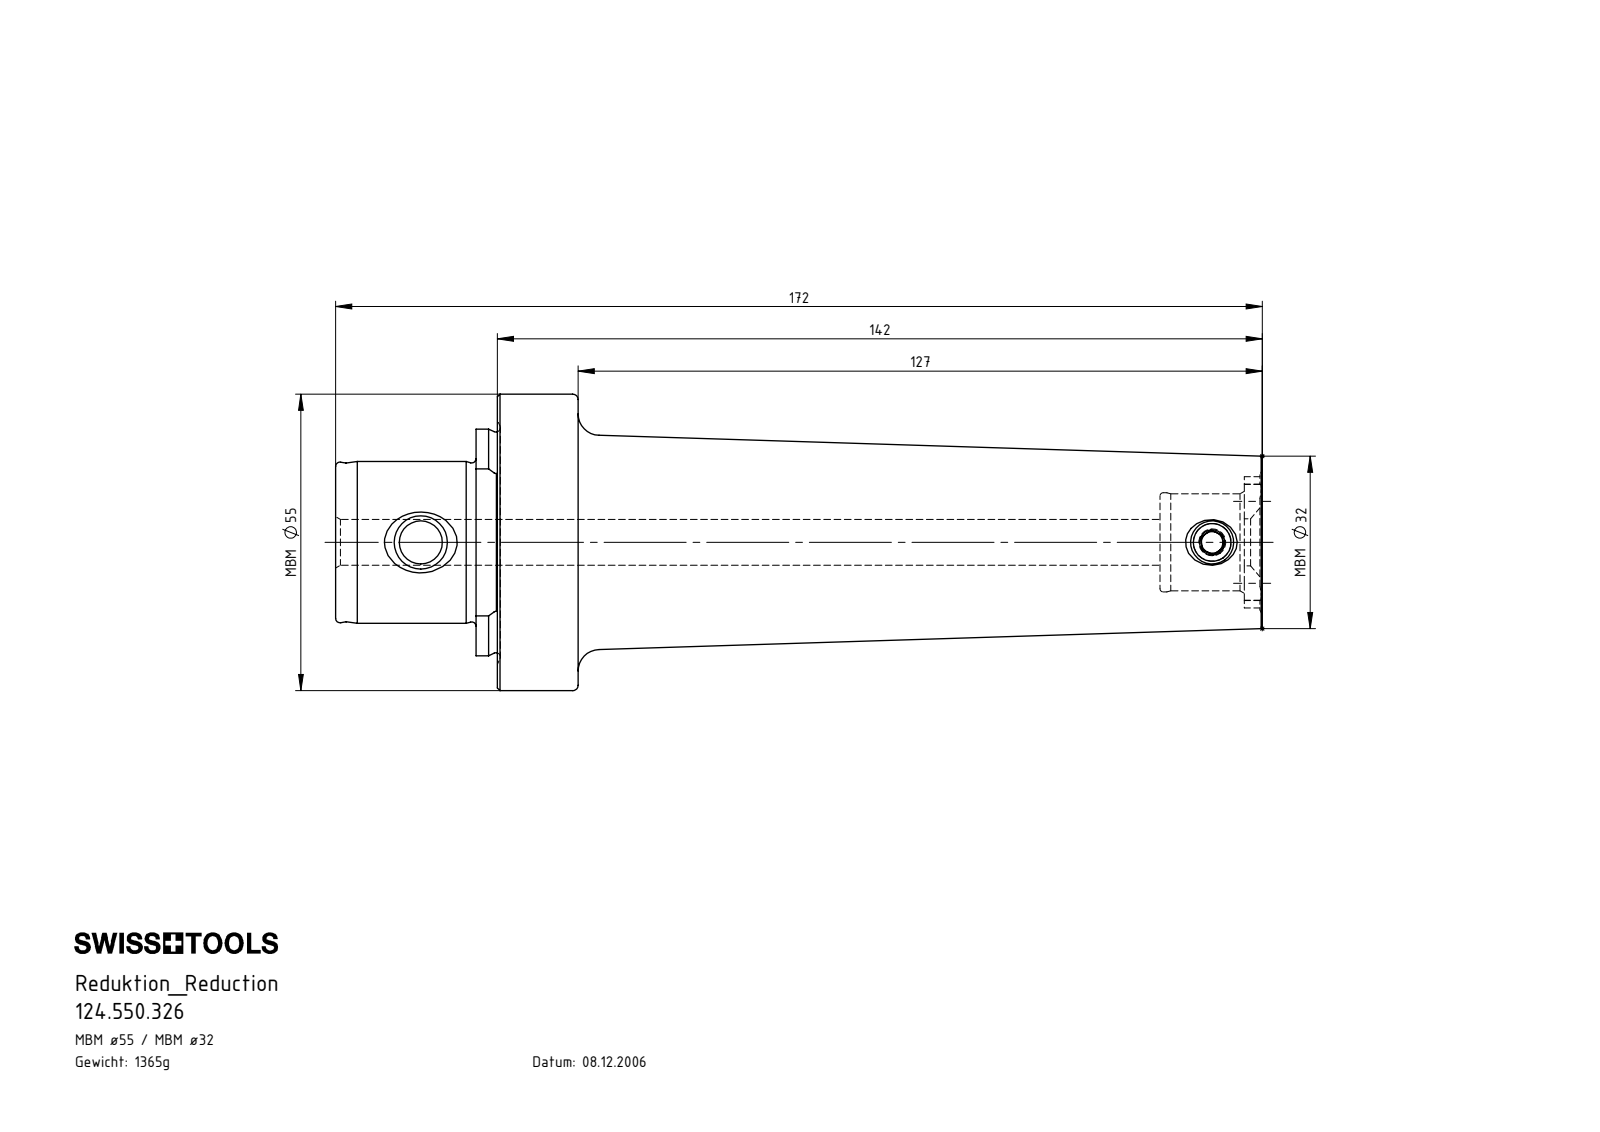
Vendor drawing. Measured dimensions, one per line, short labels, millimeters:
name: MB3-ER1.001.011_A; MB5-MB3.K01.142_C; 124.550.326
written by: SolidWorks 2017 (CONFIG_CONTROL_DESIGN)
unit: mm
bodies: 2 solids, 134 faces (33 planar, 32 cylindrical, 69 other)
size: 172 × 55 × 55
volume: 173 880 mm³; area: 29 571 mm²
holes: 1× ⌀4, 1× ⌀7, 1× ⌀8, 1× ⌀8.5, 1× ⌀18, 1× ⌀18.4
bosses: 1× ⌀55, 1× ⌀30, 1× ⌀8
rounds: 4× R3.2, 1× R10.5, 1× R12.18, 1× R21.02
face distances: 30, 26.05, 3.95, 45, 18.95, 15, 172, 145.95, 142, 127
hole spacings: 146.9
